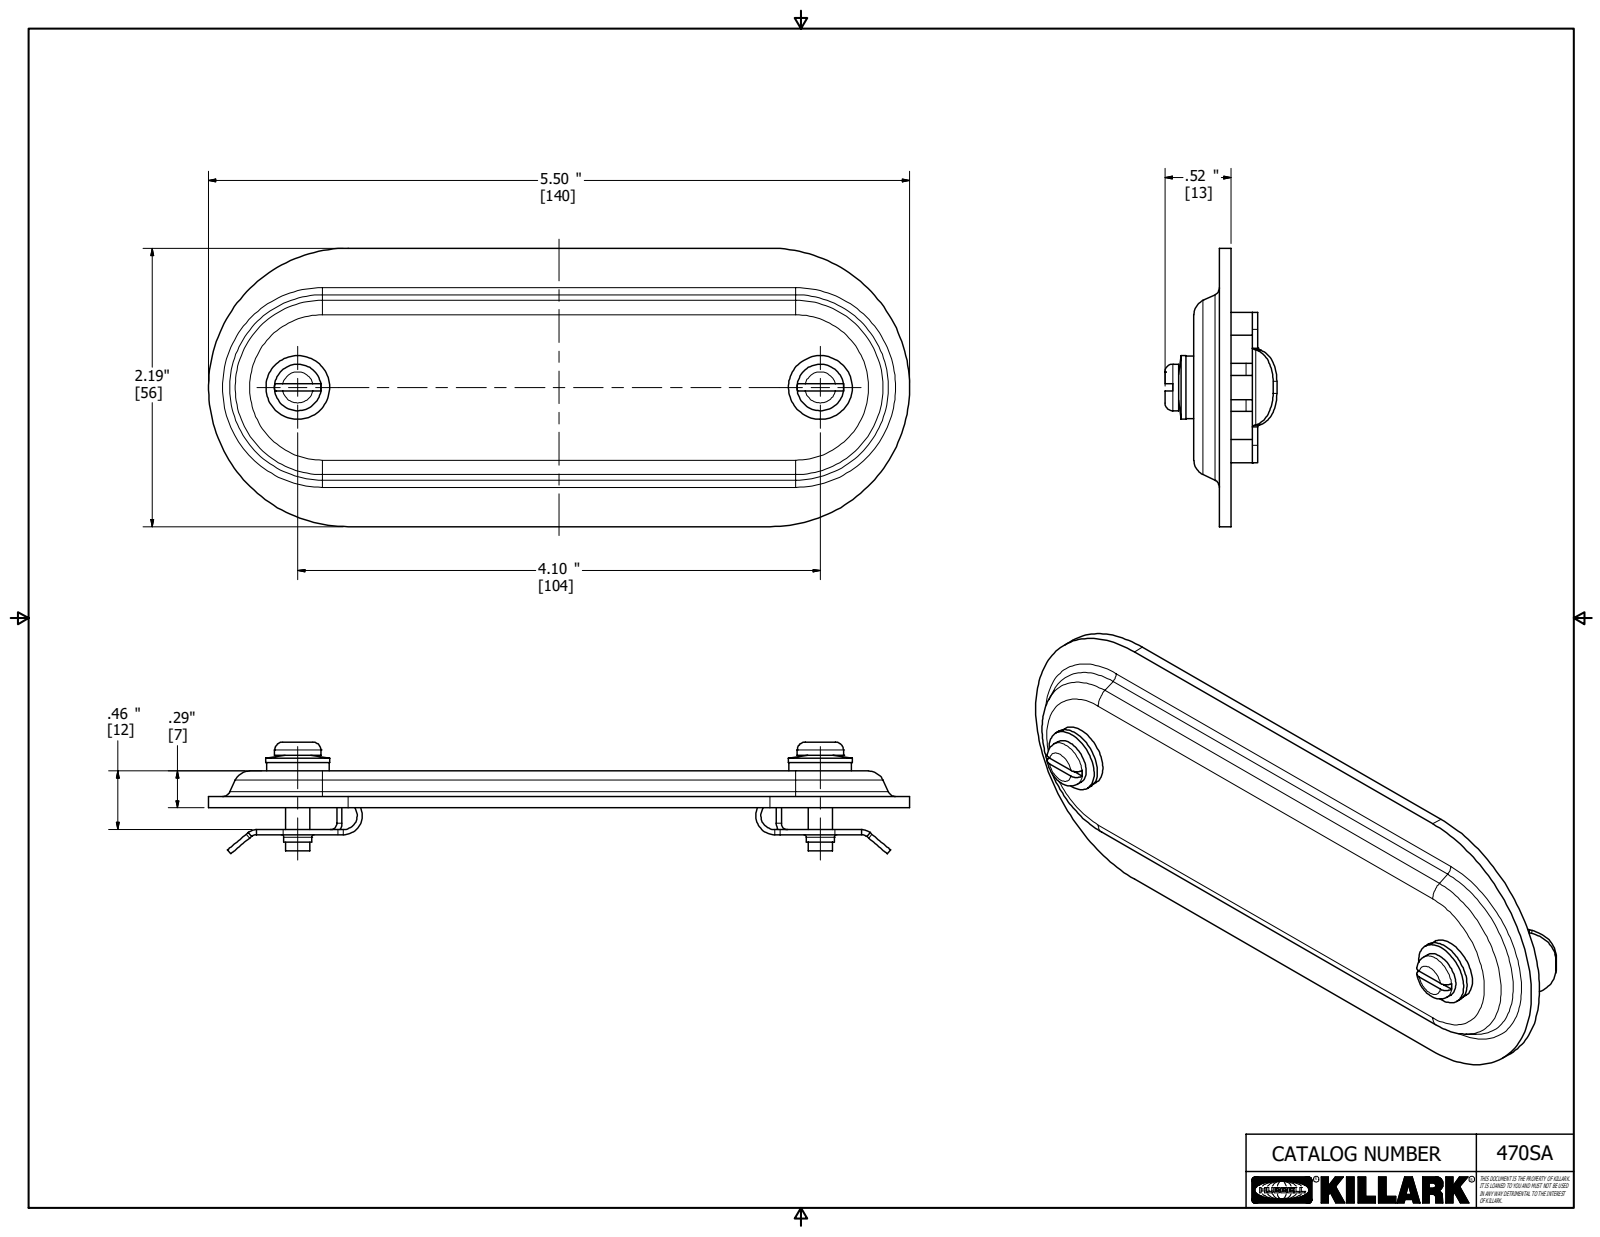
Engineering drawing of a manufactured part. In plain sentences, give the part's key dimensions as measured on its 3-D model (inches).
The part is named "470SA; 17691; 18038EAAB; 17952". Its 3-D file was written by "Autodesk Inventor 2018 (AUTOMOTIVE_DESIGN)". It is 9 solids with 220 faces: 86 planar, 74 cylindrical and 60 other. Overall it measures 5.5 by 2.187 by 0.878 inches. Its volume is 1.281 cubic inches and its surface area 34.37 square inches. Round holes: 2 of diameter 0.147, 2 of diameter 0.17, 2 of diameter 0.2, 2 of diameter 0.219. Round bosses or shafts: 2 of diameter 0.5, 2 of diameter 0.49, 2 of diameter 0.365, 2 of diameter 0.22, 2 of diameter 0.19. Partial cylindrical surfaces (rounded edges, fillets, slot ends): 10 of radius 0.06, 4 of radius 0.062, 4 of radius 0.125, 4 of radius 0.25, 4 of radius 0.75, 2 of radius 0.05, 2 of radius 0.09, 2 of radius 0.1. The main face-to-face distances are 0.09, 0.2, 0.29, 0.11, 0.04, 0.17, 0.261, 0.37, 0.461, 0.211. The hole center spacings are 4.1.
